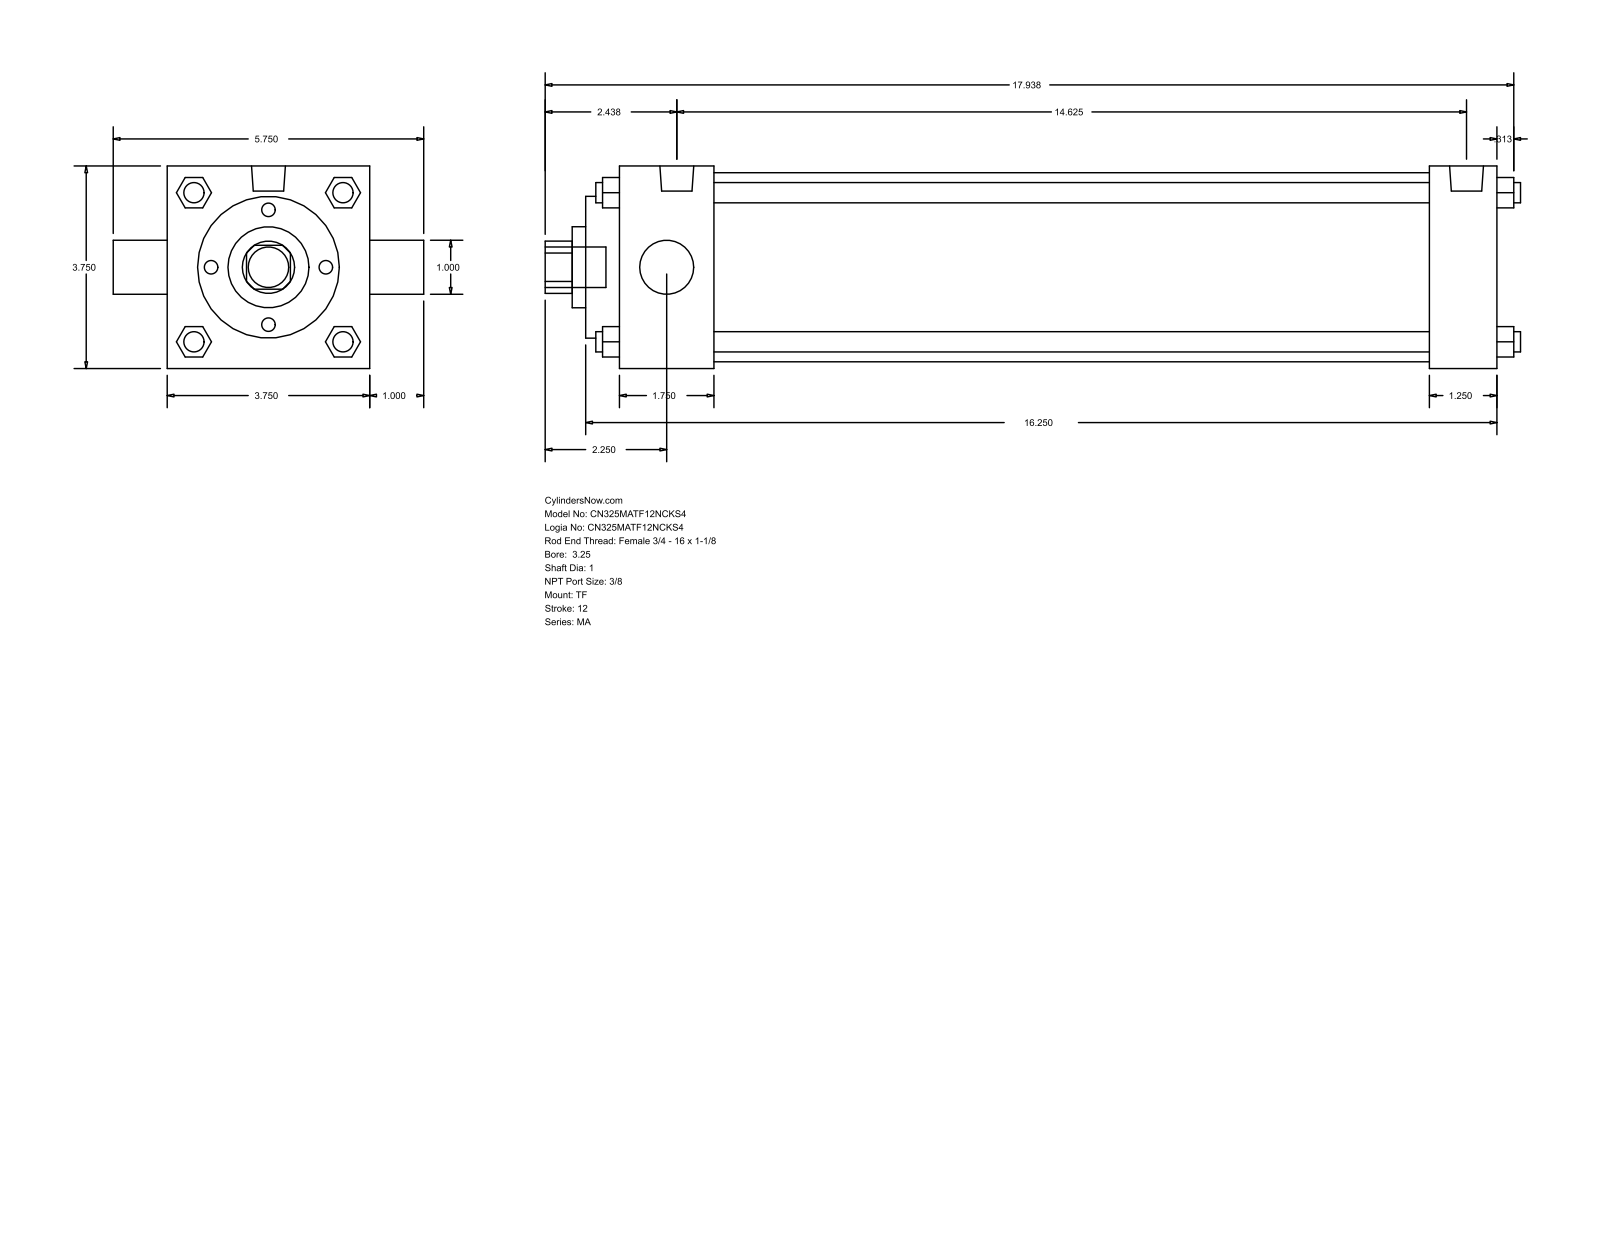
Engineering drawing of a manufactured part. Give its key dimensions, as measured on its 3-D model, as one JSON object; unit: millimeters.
{"part_name": "MA_TF__0325_1", "step_written_by": "GSSL Pune (CONFIG_CONTROL_DESIGN)", "units": "millimeters", "bodies": {"solids": 0, "faces": 122, "planar": 93, "cylindrical": 29, "other": 0}, "overall_size": [458.79, 146.05, 95.25], "round_holes": [[25.4, 2], [38.1, 1], [66.67, 1], [88.9, 1]], "round_bosses_or_shafts": [[9.53, 4], [11.11, 3], [15.93, 2], [19.05, 1]], "partial_cylinders_radius": [[12.29, 1]], "face_to_face_distances": [95.24, 412.76, 15.87, 44.46, 381.01, 336.55, 368.3, 31.75, 60.33, 396.88]}
